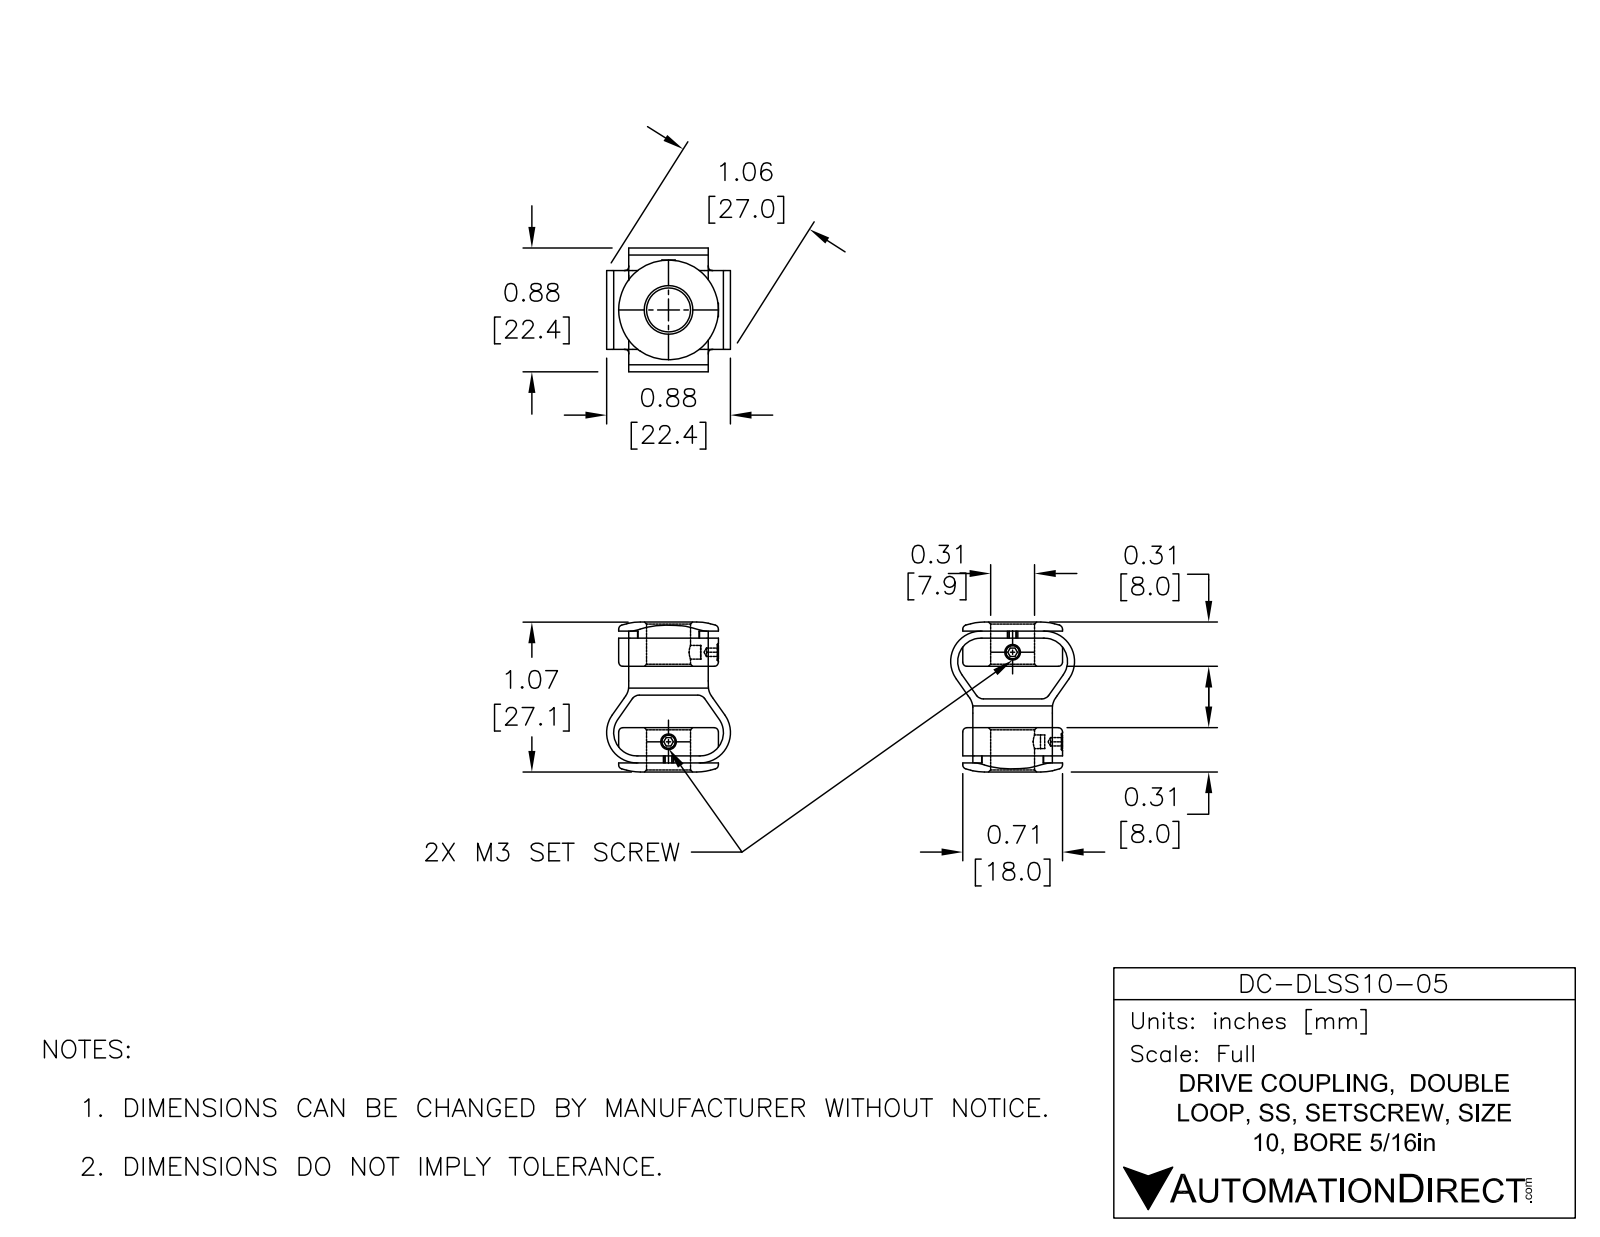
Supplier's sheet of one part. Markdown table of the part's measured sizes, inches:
| quantity | value |
| --- | --- |
| part name | DC-DLSS10-05 |
| STEP written by | SolidWorks 2015 (AUTOMOTIVE_DESIGN) |
| units | inches |
| bodies | 1 solid, 110 faces (57 planar, 28 cylindrical, 25 other) |
| overall size | 1.315 × 0.88 × 0.88 |
| volume | 0.238 in³ |
| surface area | 6.138 in² |
| round holes (diameter × count) | 0.313 × 1 |
| round bosses / shafts (diameter × count) | 0.709 × 1 |
| partial cylindrical surfaces (radius × count) | 0.165 × 4, 0.215 × 4, 0.22 × 1 |
| main face-to-face distances | 0.05, 0.645, 0.67, 0.695, 1.315, 0.62, 0.481, 0.457, 0.213, 1.102 |
